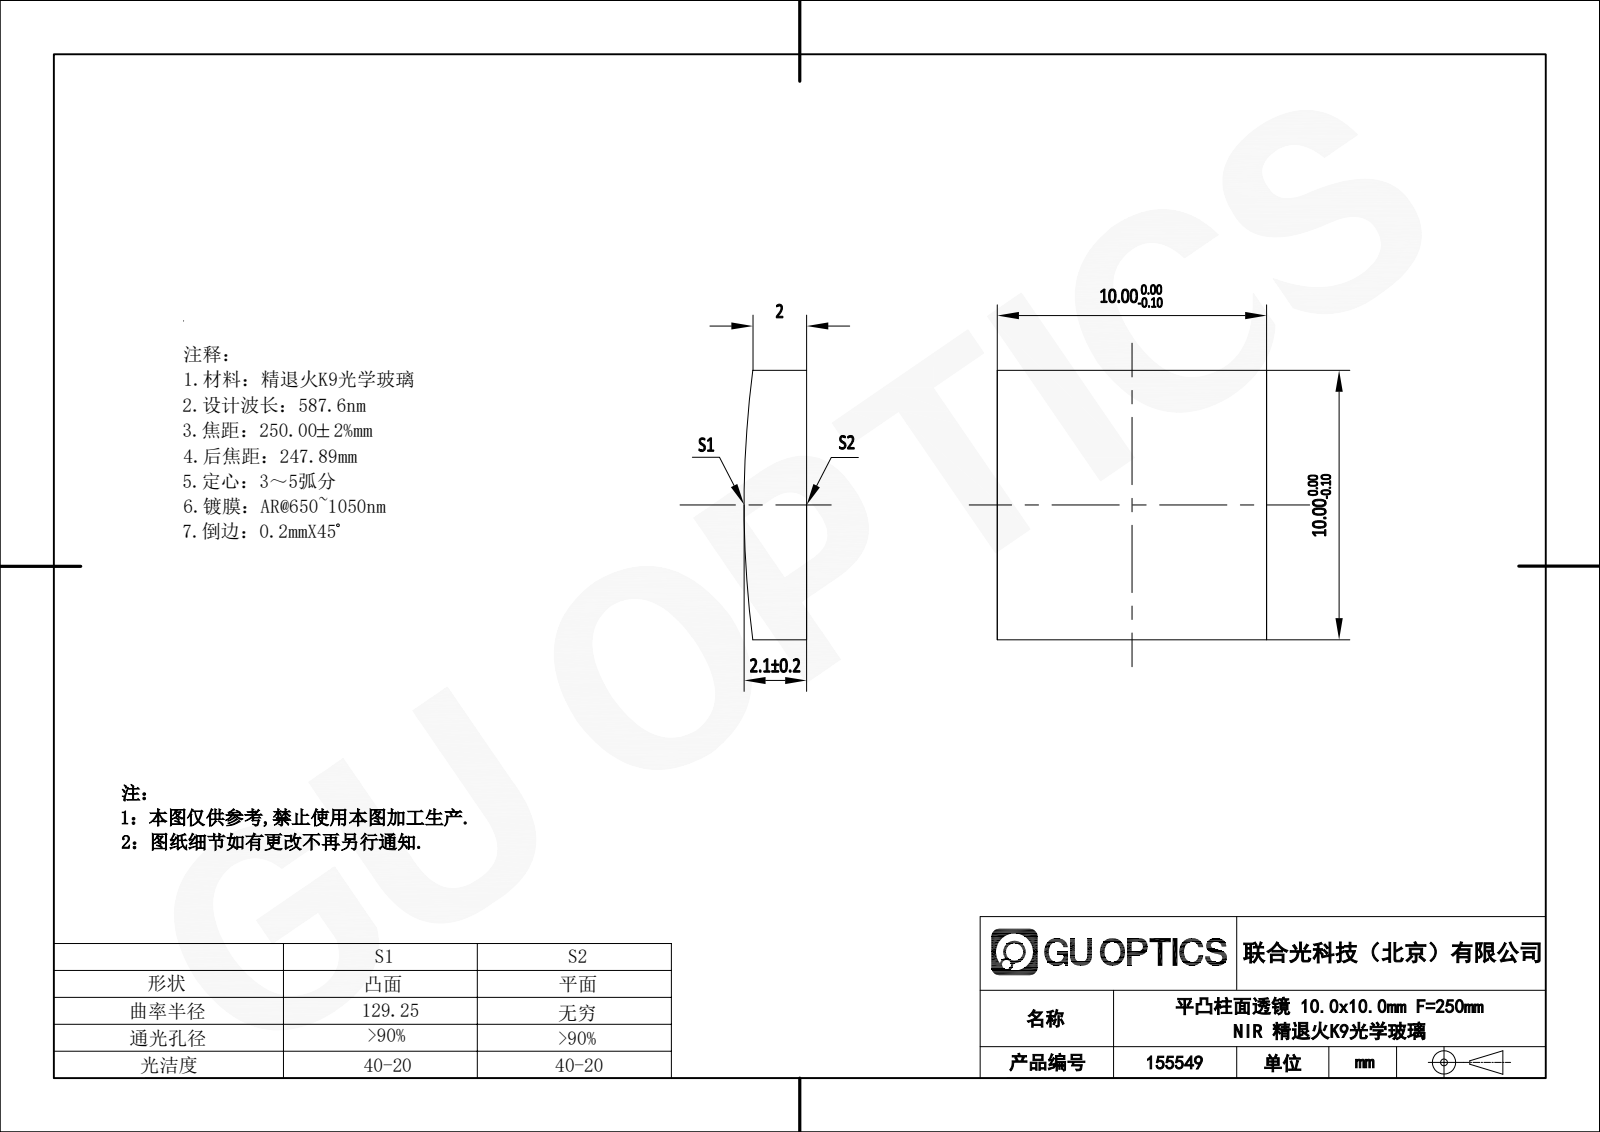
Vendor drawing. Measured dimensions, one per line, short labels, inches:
name: 155525
written by: SolidWorks 2020 (CONFIG_CONTROL_DESIGN)
unit: in
bodies: 1 solid, 7 faces (5 planar, 2 cylindrical, 0 other)
size: 0.394 × 0.394 × 0.083
volume: 0.013 in³; area: 0.436 in²
rounds: 1× R5.089
face distances: 0.394
